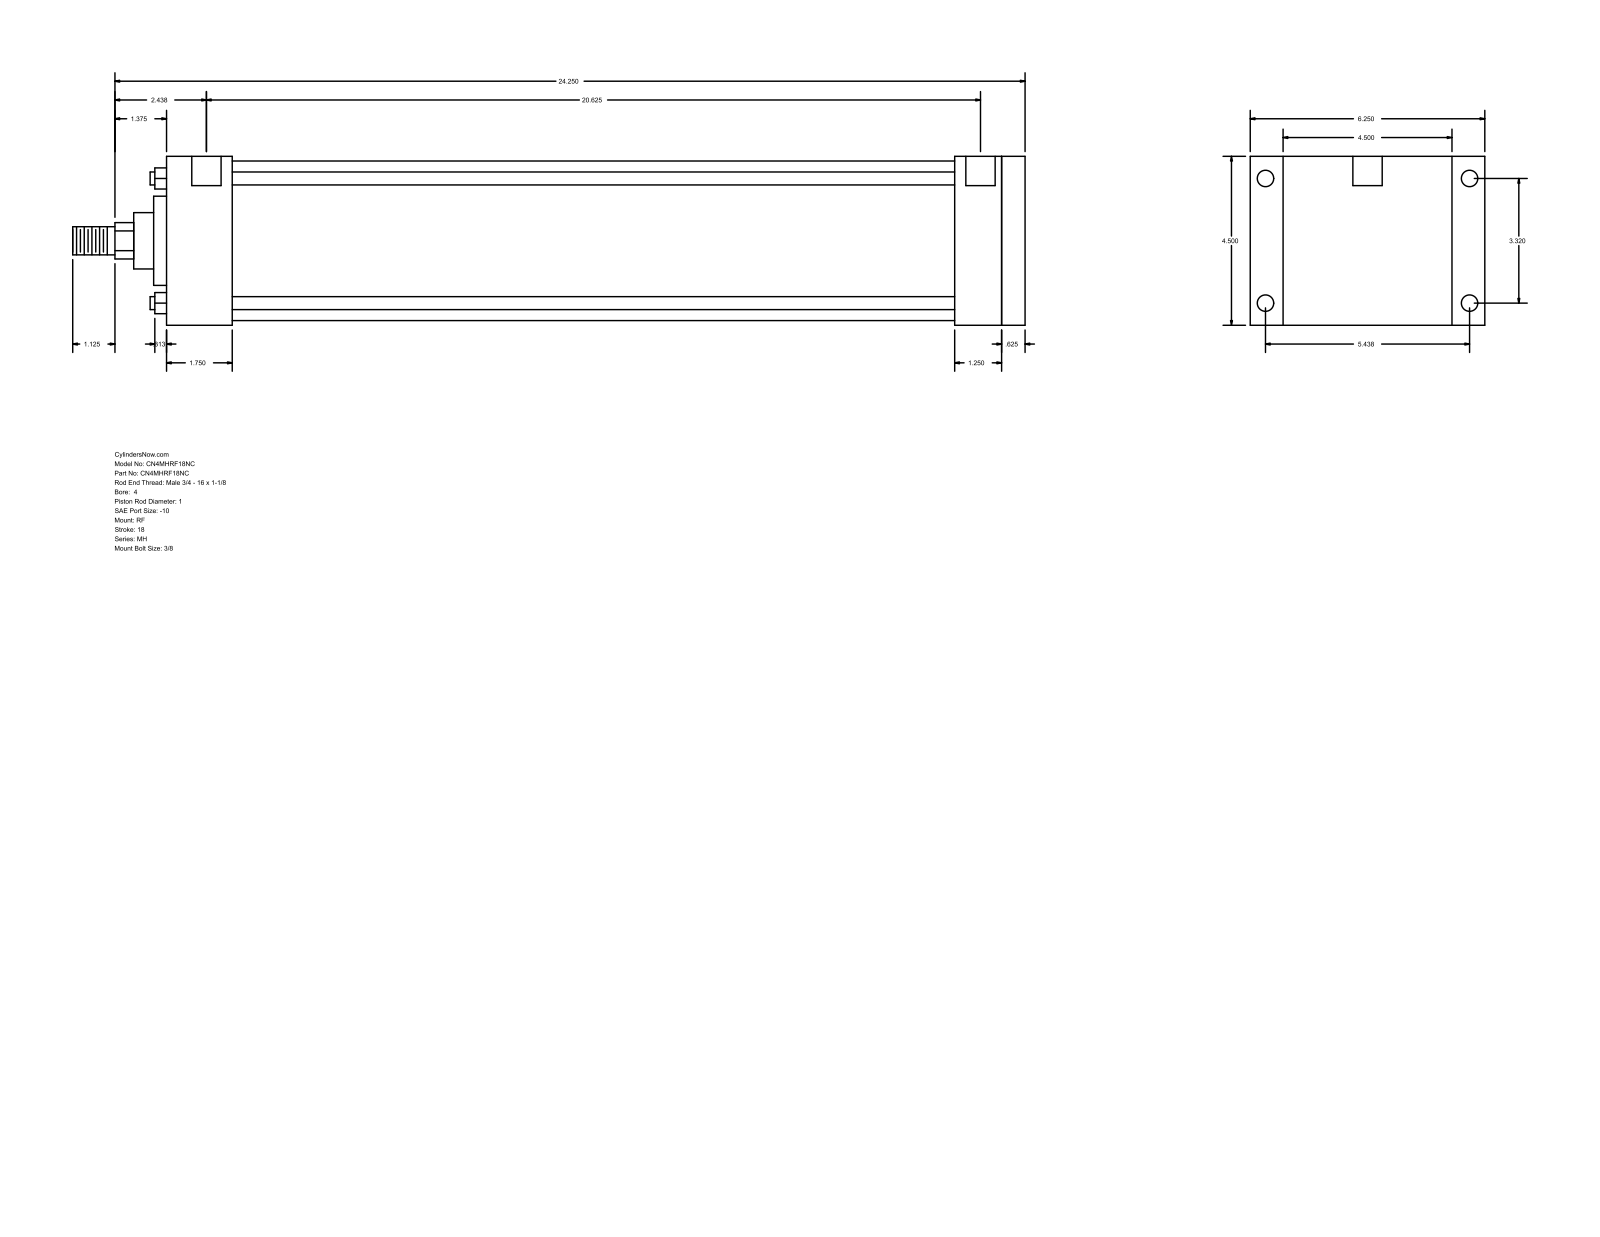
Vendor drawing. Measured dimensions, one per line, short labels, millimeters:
name: MH_RF__0400_1
written by: GSSL Pune (CONFIG_CONTROL_DESIGN)
unit: mm
bodies: 0 solids, 94 faces (65 planar, 29 cylindrical, 0 other)
size: 644.52 × 158.75 × 114.3
holes: 4× ⌀8.73, 4× ⌀11.13, 2× ⌀19.84
bosses: 4× ⌀8.76, 1× ⌀107.95, 1× ⌀60.33, 1× ⌀38.1, 1× ⌀25.4, 1× ⌀19.05
rounds: 1× R12.29
face distances: 114.3, 581.03, 565.16, 15.87, 44.46, 520.7, 536.57, 533.41, 488.95, 31.75
hole spacings: 84.32, 138.12, 161.82, 527.05, 1.58, 1.59, 523.88, 525.46
